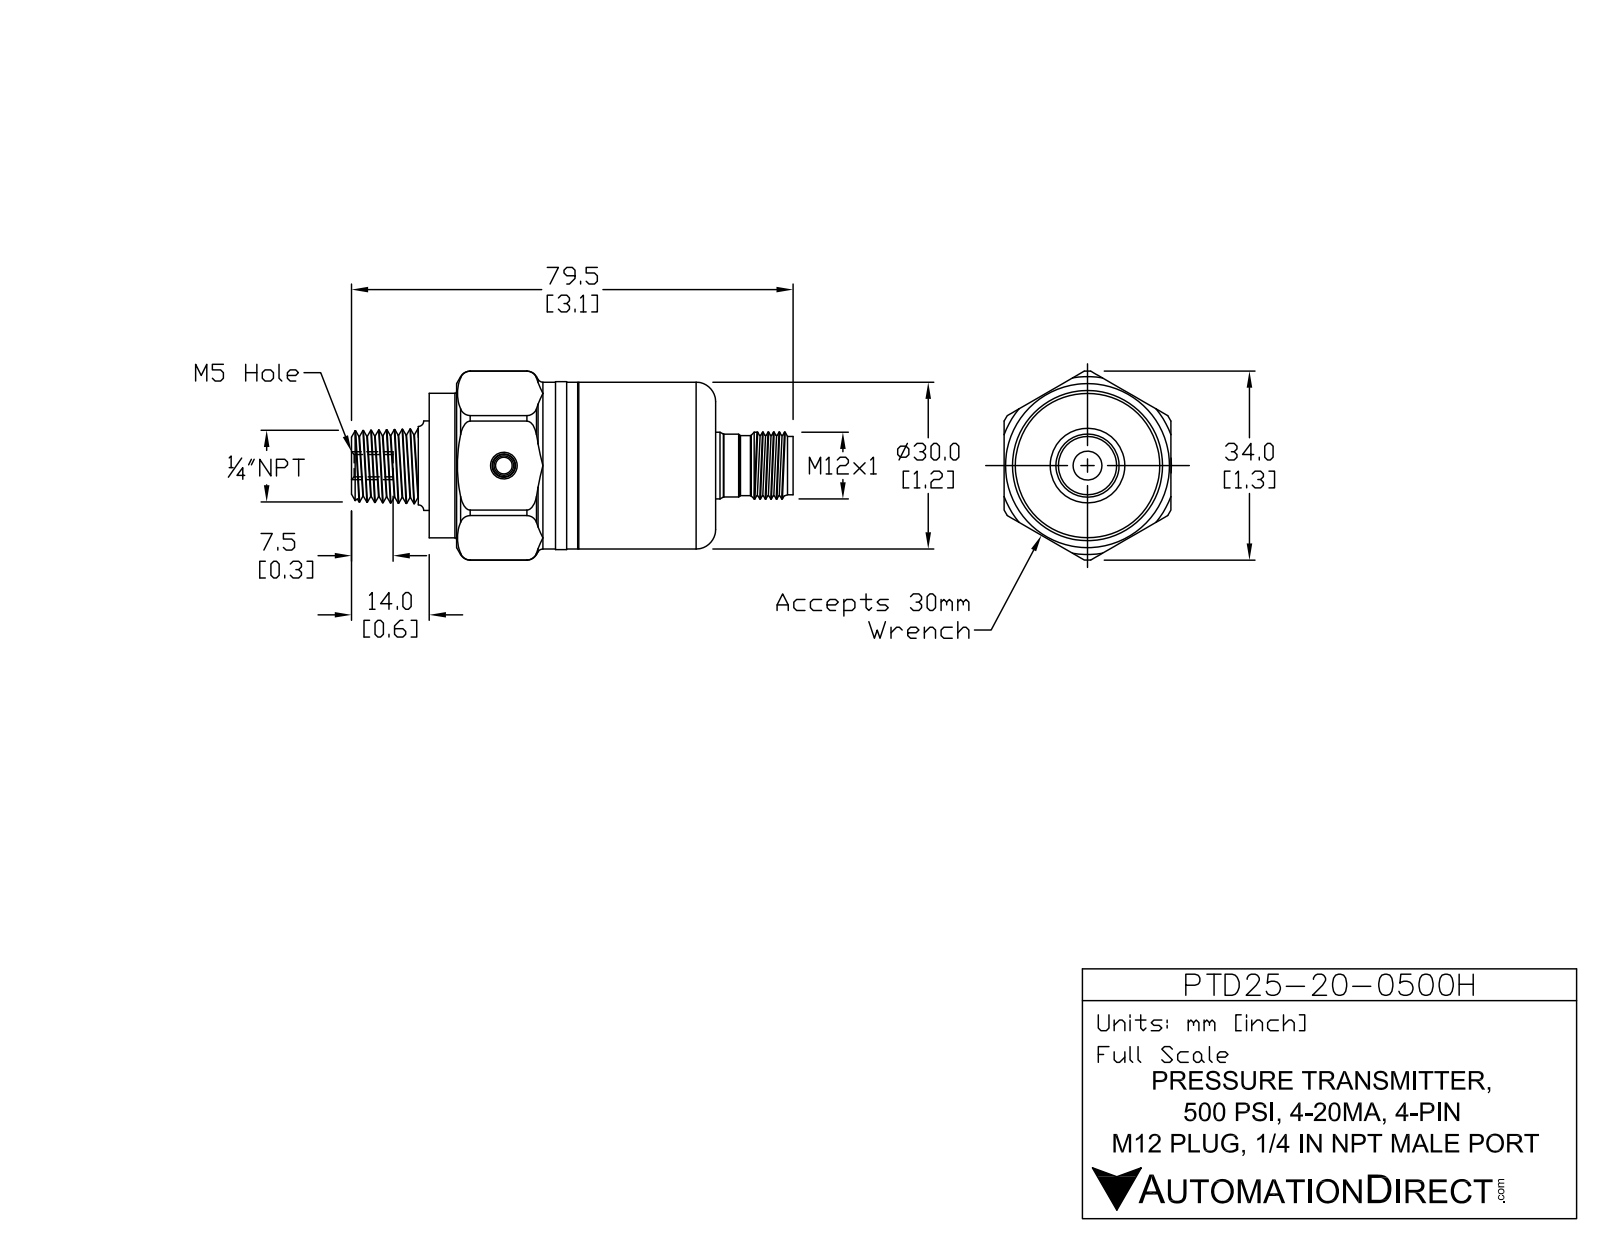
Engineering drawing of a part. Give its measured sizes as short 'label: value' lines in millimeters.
name: PTD25-20-0500H
written by: SolidWorks 2017 (AUTOMOTIVE_DESIGN)
unit: mm
bodies: 1 solid, 124 faces (36 planar, 59 cylindrical, 29 other)
size: 79.5 × 33.78 × 31.7
volume: 39 212 mm³; area: 8 088 mm²
holes: 1× ⌀4, 1× ⌀8.5
bosses: 1× ⌀30.05, 1× ⌀30, 1× ⌀25.96, 1× ⌀14, 1× ⌀13.5, 1× ⌀12
rounds: 1× R3.76, 1× R16.95
face distances: 51, 29.98, 30, 48, 3, 65, 17, 14, 30.01, 5.65
